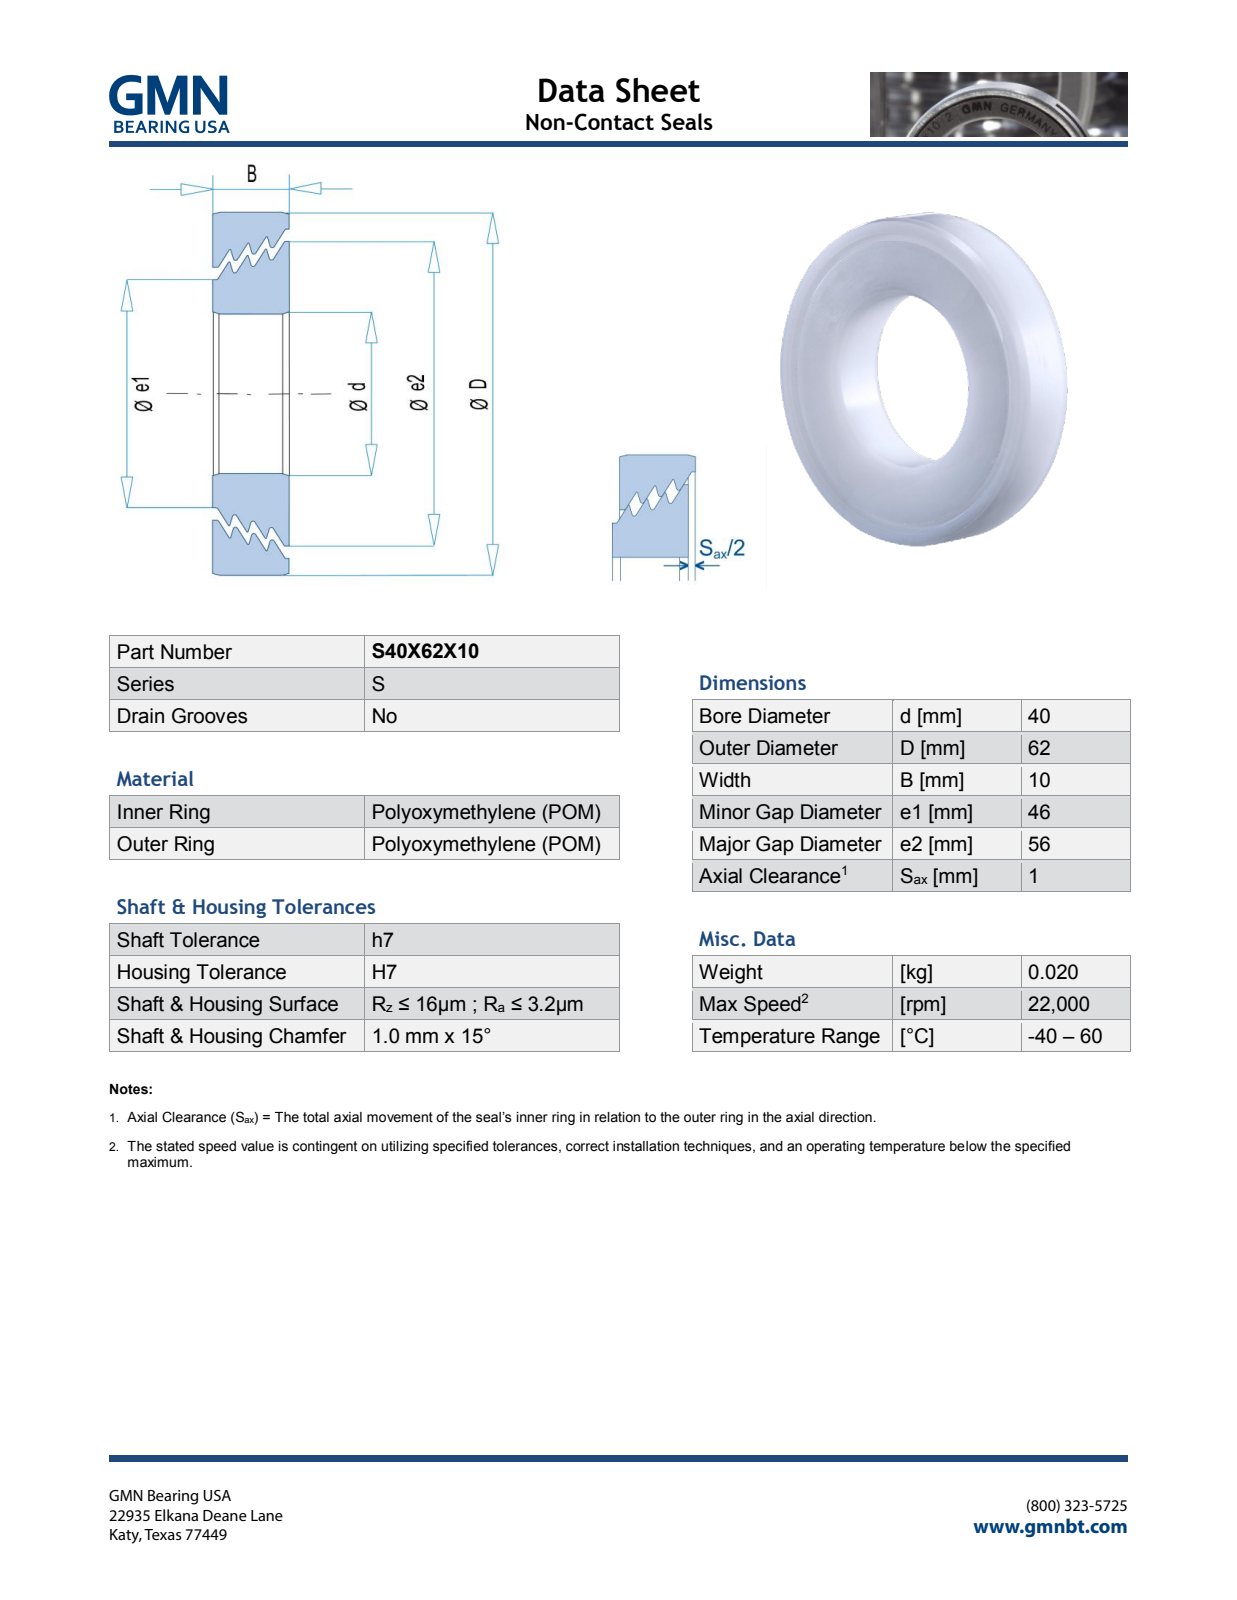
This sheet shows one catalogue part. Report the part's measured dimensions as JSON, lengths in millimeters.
{"part_name": "S40X62X10_PRT", "step_written_by": "PRO/ENGINEER BY PARAMETRIC TECHNOLOGY CORPORATION, 2013150 (AUTOMOTIVE_DESIGN)", "units": "millimeters", "bodies": {"solids": 2, "faces": 646, "planar": 566, "cylindrical": 12, "other": 68}, "overall_size": [62, 62, 10.07], "volume_mm3": 16212, "surface_area_mm2": 13044, "round_holes": [[40, 1], [47.63, 1], [57.63, 1]], "round_bosses_or_shafts": [[62, 1], [56, 1], [46, 1]], "face_to_face_distances": [10, 10.07, 2.13, 1.86, 1.51, 1.6, 1.87, 1.78, 0.95, 0.91]}
